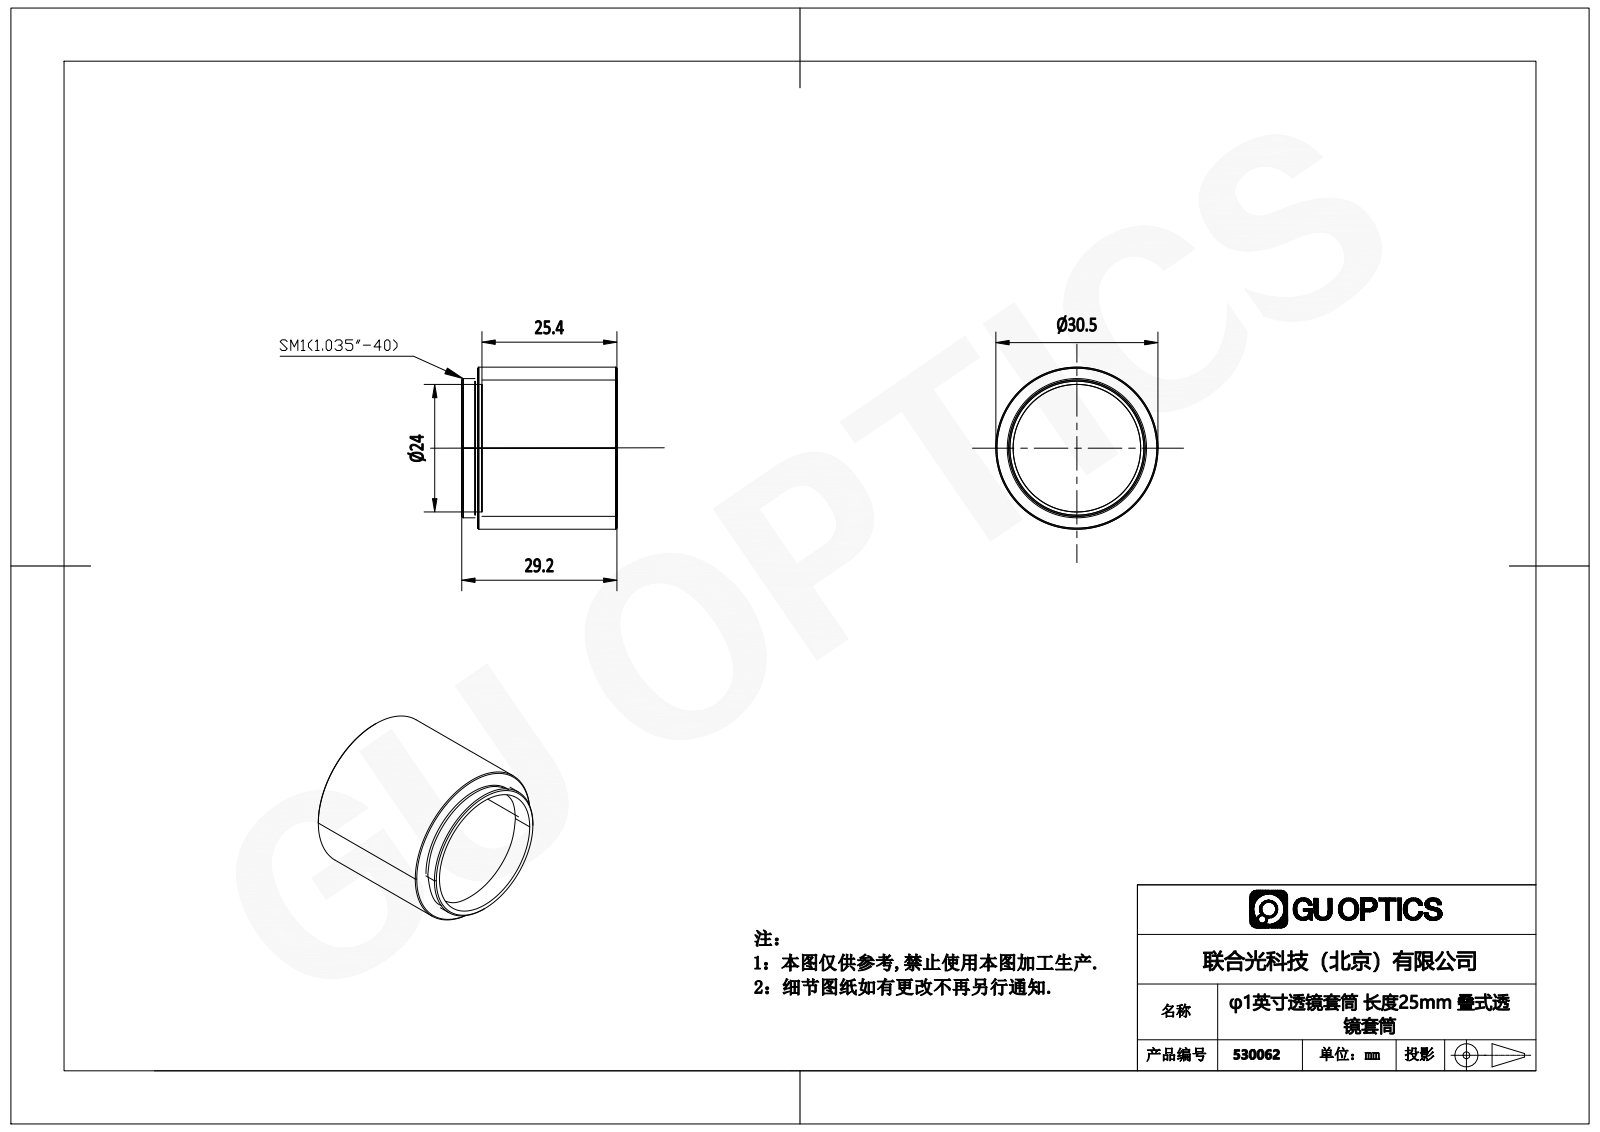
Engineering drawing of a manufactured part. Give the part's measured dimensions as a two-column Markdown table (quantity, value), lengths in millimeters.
| quantity | value |
| --- | --- |
| STEP written by | SolidWorks 2018 (AUTOMOTIVE_DESIGN) |
| units | millimeters |
| bodies | 0 solids, 34 faces (11 planar, 12 cylindrical, 11 other) |
| overall size | 30.5 × 30.5 × 29.2 |
| round holes (diameter × count) | 23.01 × 1, 24 × 1, 25.65 × 1 |
| round bosses / shafts (diameter × count) | 30.5 × 1, 26.2 × 1, 25.2 × 1 |
| main face-to-face distances | 26.2, 1, 25.2, 29.2, 28.2, 3, 1.7, 0.7, 24.5, 27.5 |
